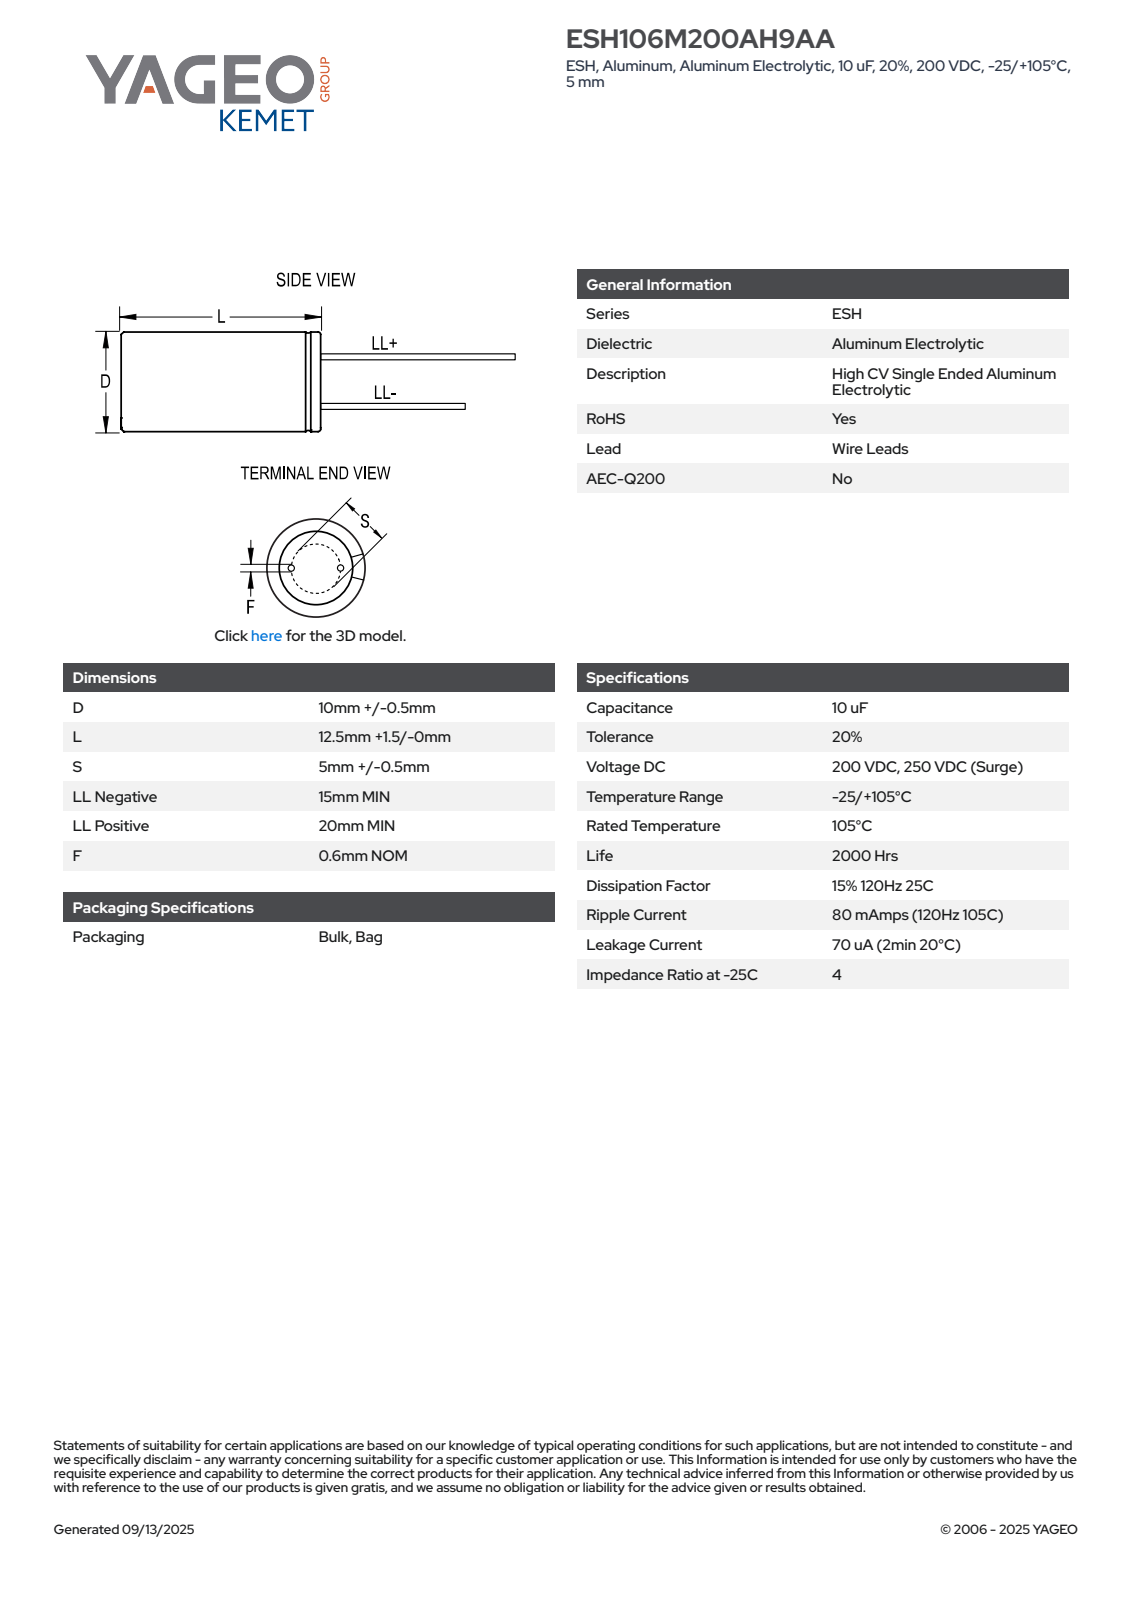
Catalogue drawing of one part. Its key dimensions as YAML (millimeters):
part_name: "CAR_KLP_10X12.5_D10.5L14S5F0.6"
step_written_by: "SolidWorks 2014 (AUTOMOTIVE_DESIGN)"
units: millimeters
bodies: {solids: 4, faces: 75, planar: 61, cylindrical: 8, other: 6}
overall_size: [34.01, 10.5, 10.5]
volume: 1210
surface_area: 726
round_bosses_or_shafts:
  - {diameter: 0.6, count: 2}
  - {diameter: 10.5, count: 1}
face_to_face_distances: [14, 14.01, 29.01, 34.01, 29, 34, 15, 20, 5, 1.41]
